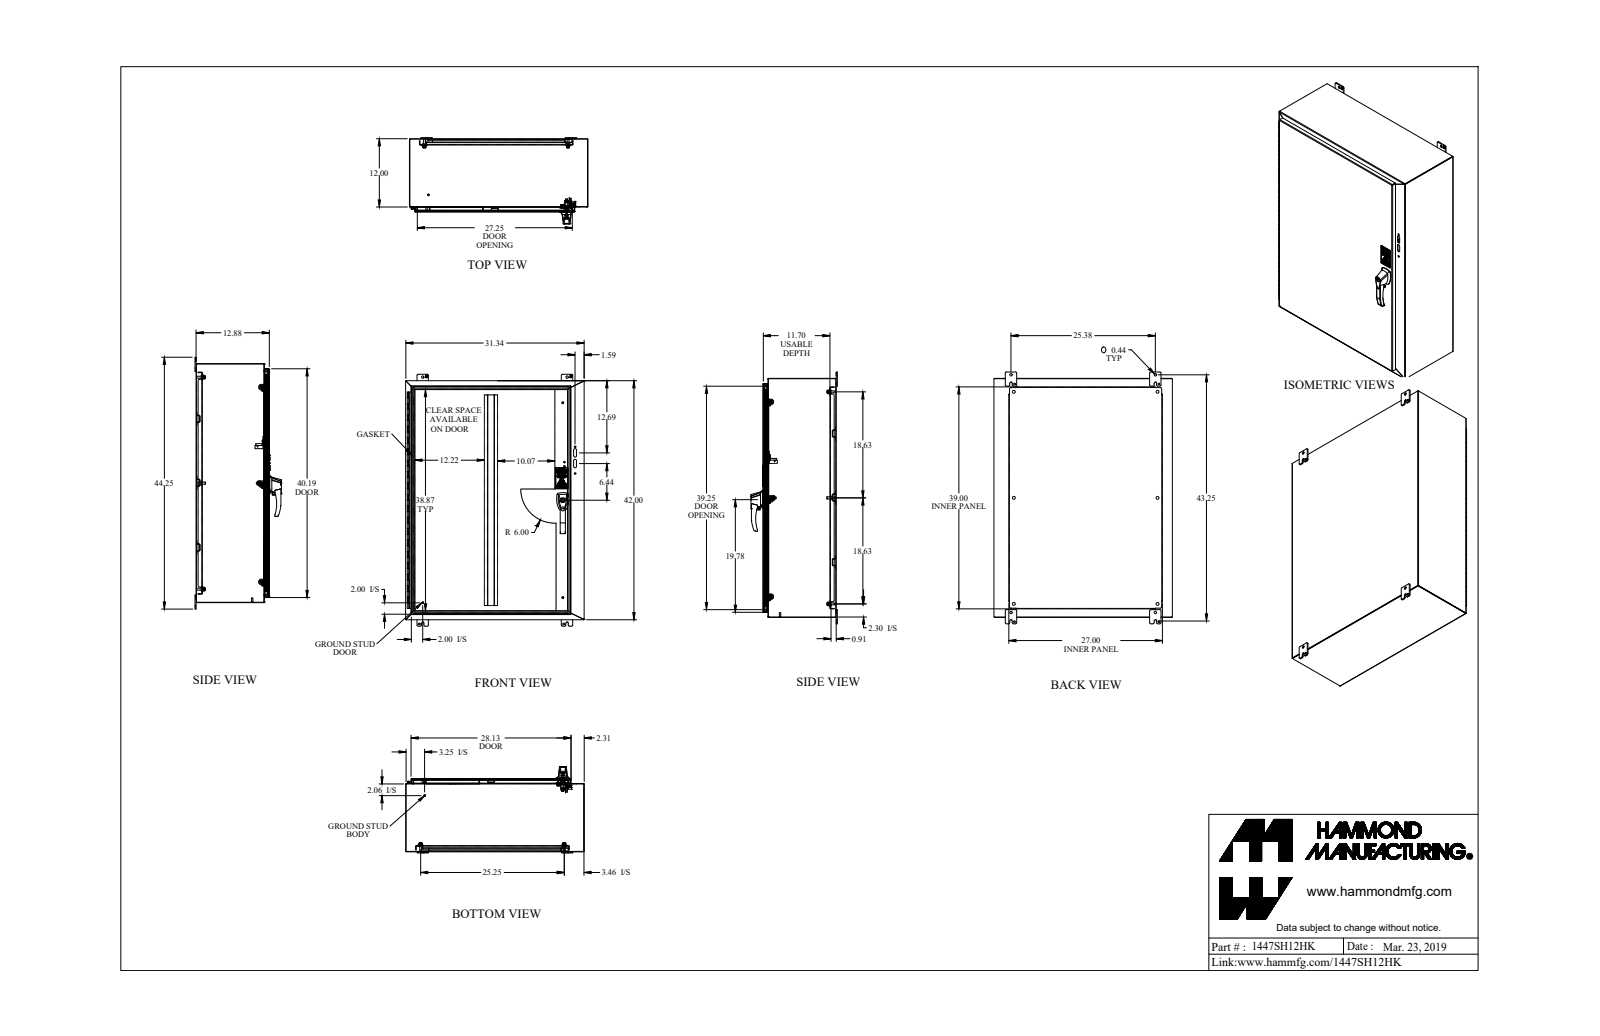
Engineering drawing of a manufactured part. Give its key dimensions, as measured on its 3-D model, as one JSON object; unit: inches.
{"part_name": "1447SH12HK_Default", "step_written_by": "SolidWorks 2019 (CONFIG_CONTROL_DESIGN)", "units": "inches", "bodies": {"solids": 69, "faces": 1974, "planar": 1004, "cylindrical": 783, "other": 187}, "overall_size": [44.25, 31.375, 15.177], "volume_in3": 507, "surface_area_in2": 13010, "round_holes": [[0.176, 6], [0.313, 6], [0.5, 6], [0.307, 4], [0.437, 4], [0.445, 4], [0.25, 3], [0.265, 3], [0.413, 3], [0.156, 2], [0.173, 2], [0.196, 2]], "round_bosses_or_shafts": [[0.375, 11], [0.25, 9], [1, 7], [0.65, 6], [0.33, 6], [0.156, 6], [0.63, 2], [0.51, 2]], "partial_cylinders_radius": [[0.188, 35], [0.25, 35], [0.036, 18], [0.108, 18], [0.116, 16], [0.125, 16], [0.03, 10], [0.218, 8]], "face_to_face_distances": [0.072, 12.803, 12.731, 12.875, 0.095, 11.771, 11.699, 1.032, 1.104, 11.866], "hole_center_spacings": [25.25, 31.376, 18.625, 25.375, 1.11, 31.175, 1.535, 1.735]}
